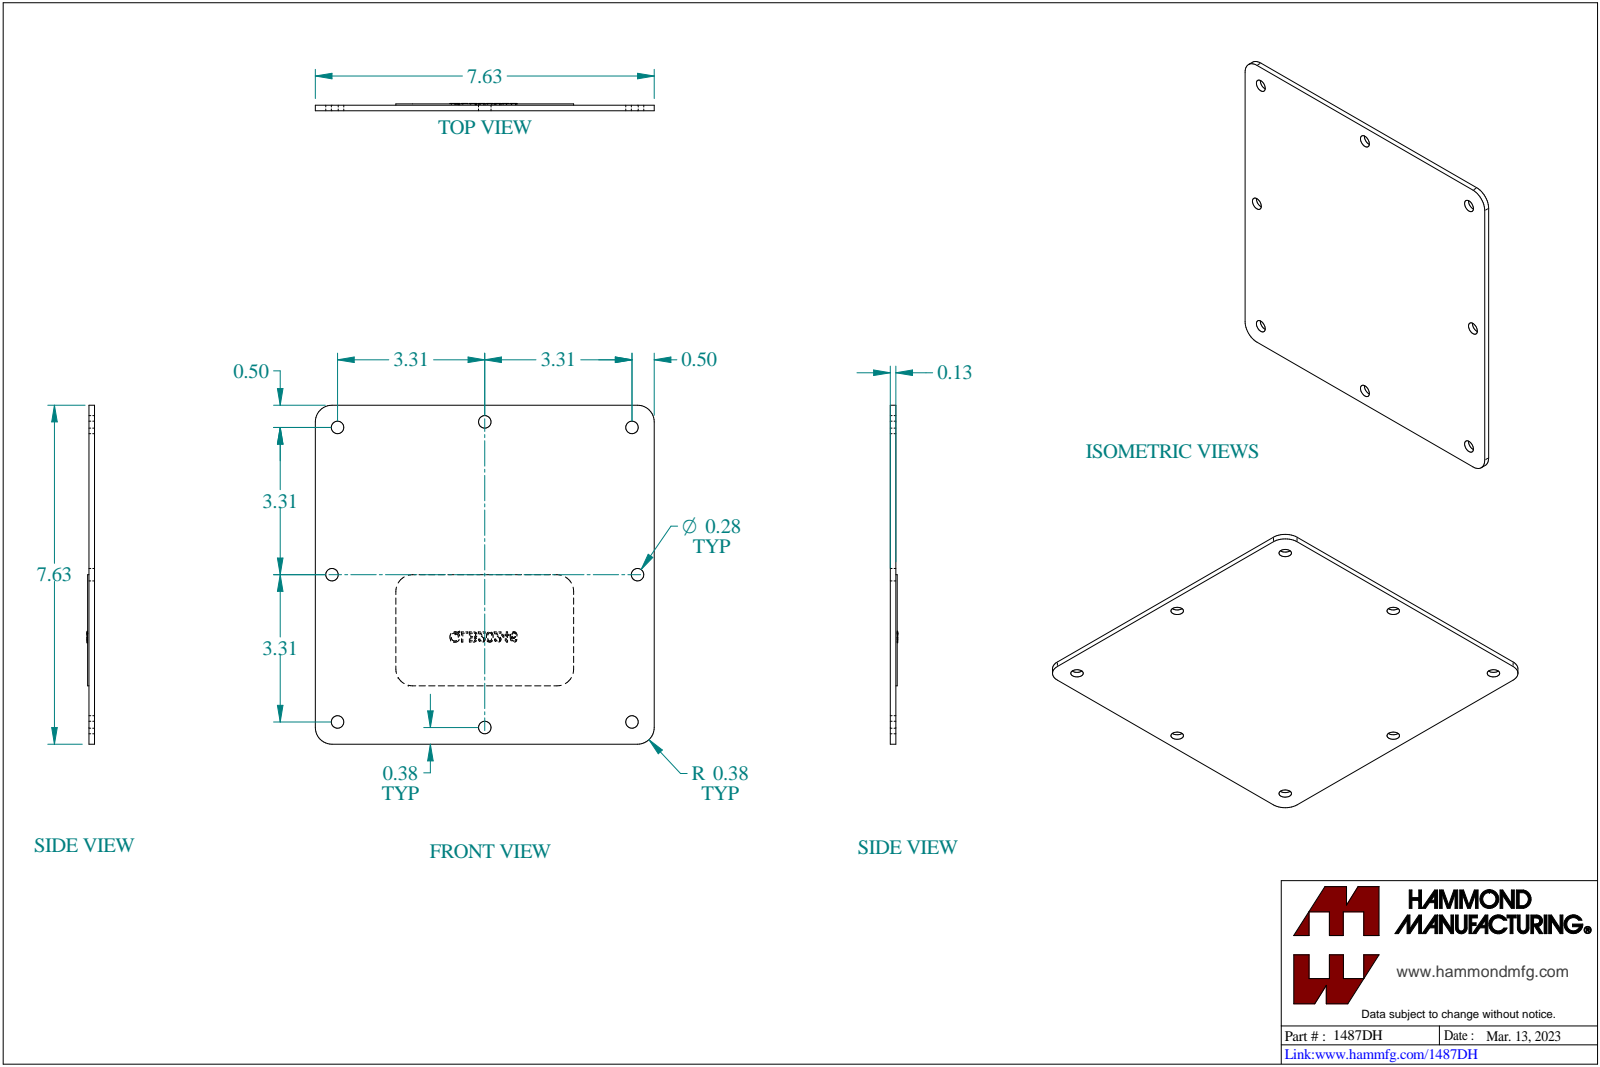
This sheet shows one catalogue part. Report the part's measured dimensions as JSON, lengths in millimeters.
{"part_name": "1487DH", "step_written_by": "SolidWorks 2023 (CONFIG_CONTROL_DESIGN)", "units": "millimeters", "bodies": {"solids": 2, "faces": 60, "planar": 16, "cylindrical": 44, "other": 0}, "overall_size": [193.7, 193.7, 6.4], "volume_mm3": 163500, "surface_area_mm2": 110800, "round_holes": [[7.1, 8]], "partial_cylinders_radius": [[6.4, 4], [9.5, 4]], "face_to_face_distances": [3.2, 6.4, 3.2, 193.7, 21.4, 172.3, 150.9], "hole_center_spacings": [84.2, 191, 123.5, 168.3, 174.6, 238]}
